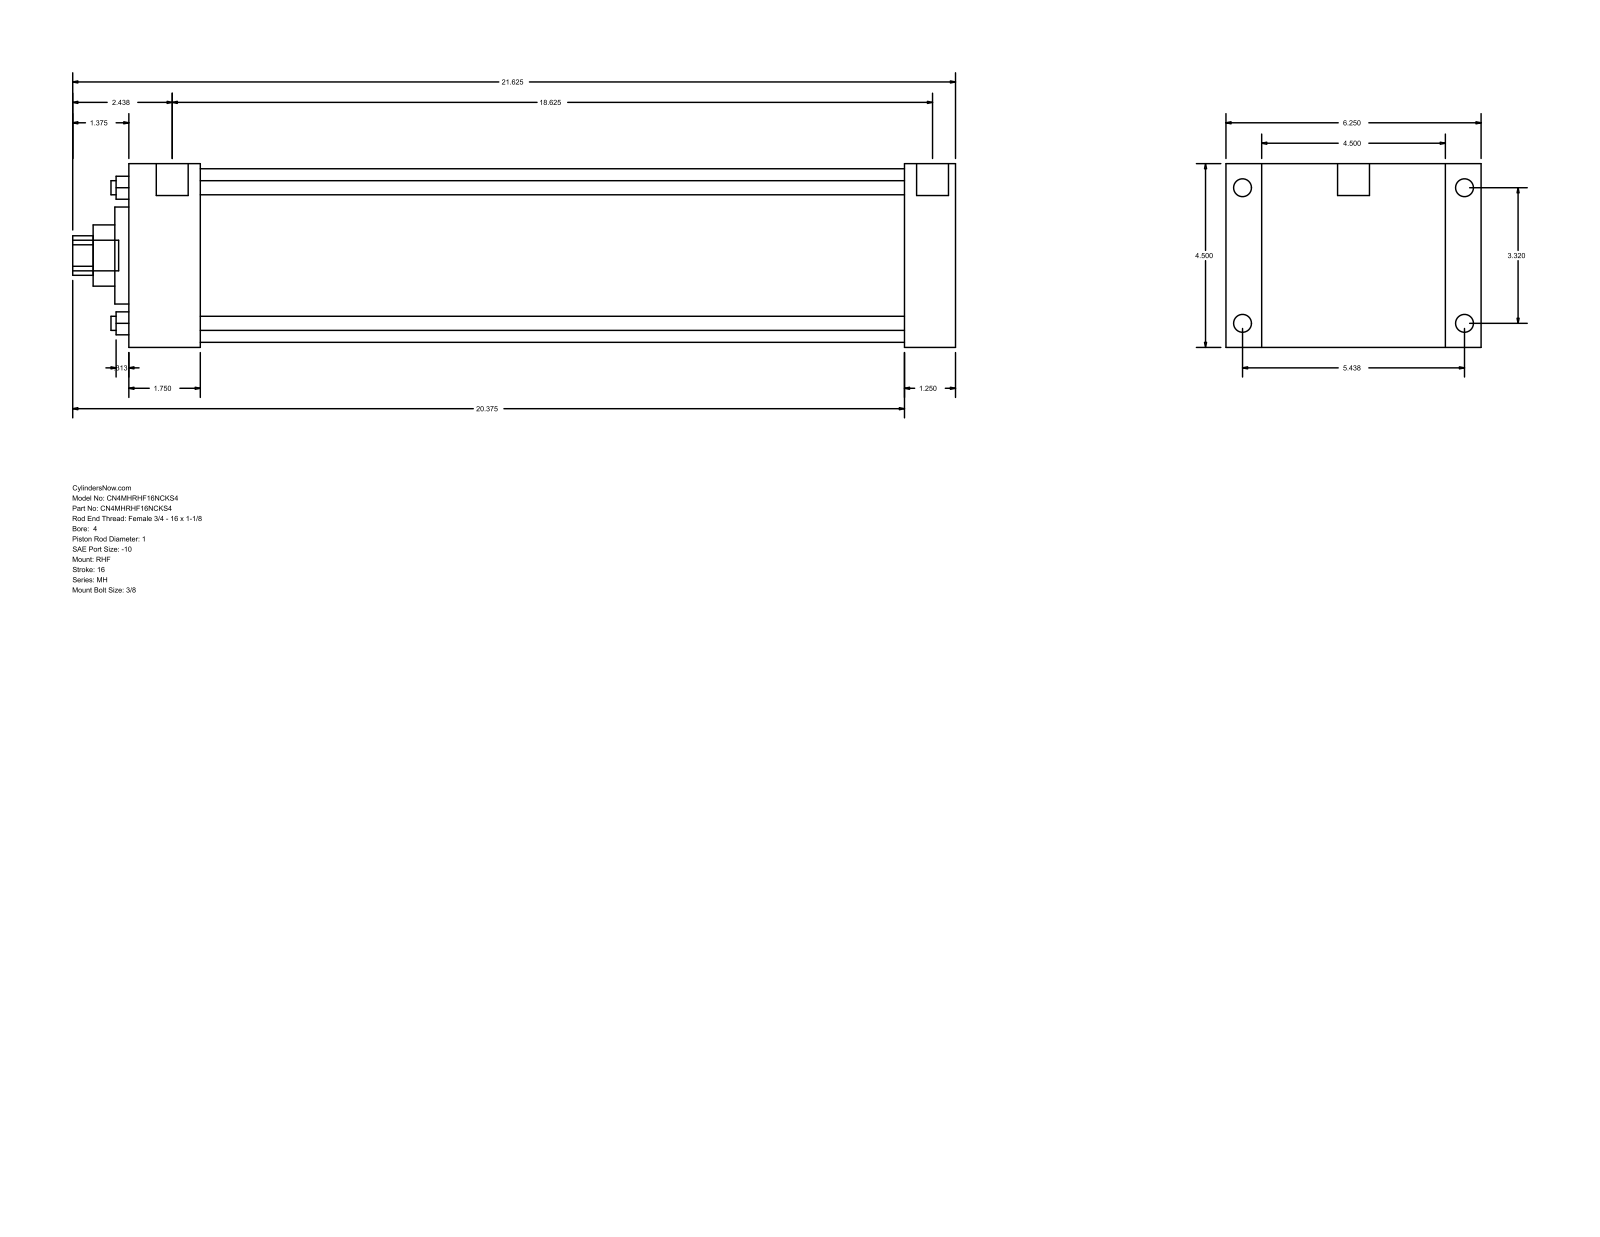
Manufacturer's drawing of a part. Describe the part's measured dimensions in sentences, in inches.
The part is named "MH_RHF__0400_1". Its 3-D file was written by "GSSL Pune (CONFIG_CONTROL_DESIGN)". It is 0 solids with 90 faces: 61 planar, 29 cylindrical and 0 other. Overall it measures 21.625 by 6.25 by 4.5 inches. Round holes: 4 of diameter 0.345, 1 of diameter 1, 1 of diameter 1.5, 1 of diameter 2.375, 1 of diameter 4.25. Round bosses or shafts: 4 of diameter 0.438, 4 of diameter 0.344, 2 of diameter 0.781, 1 of diameter 0.75. Partial cylindrical surfaces (rounded edges, fillets, slot ends): 1 of radius 0.484. The main face-to-face distances are 4.5, 20.25, 19, 1.25, 0.875, 5.375, 1.75, 17.25, 18.5, 6.25. The hole center spacings are 2.347, 3.32, 4.695.
